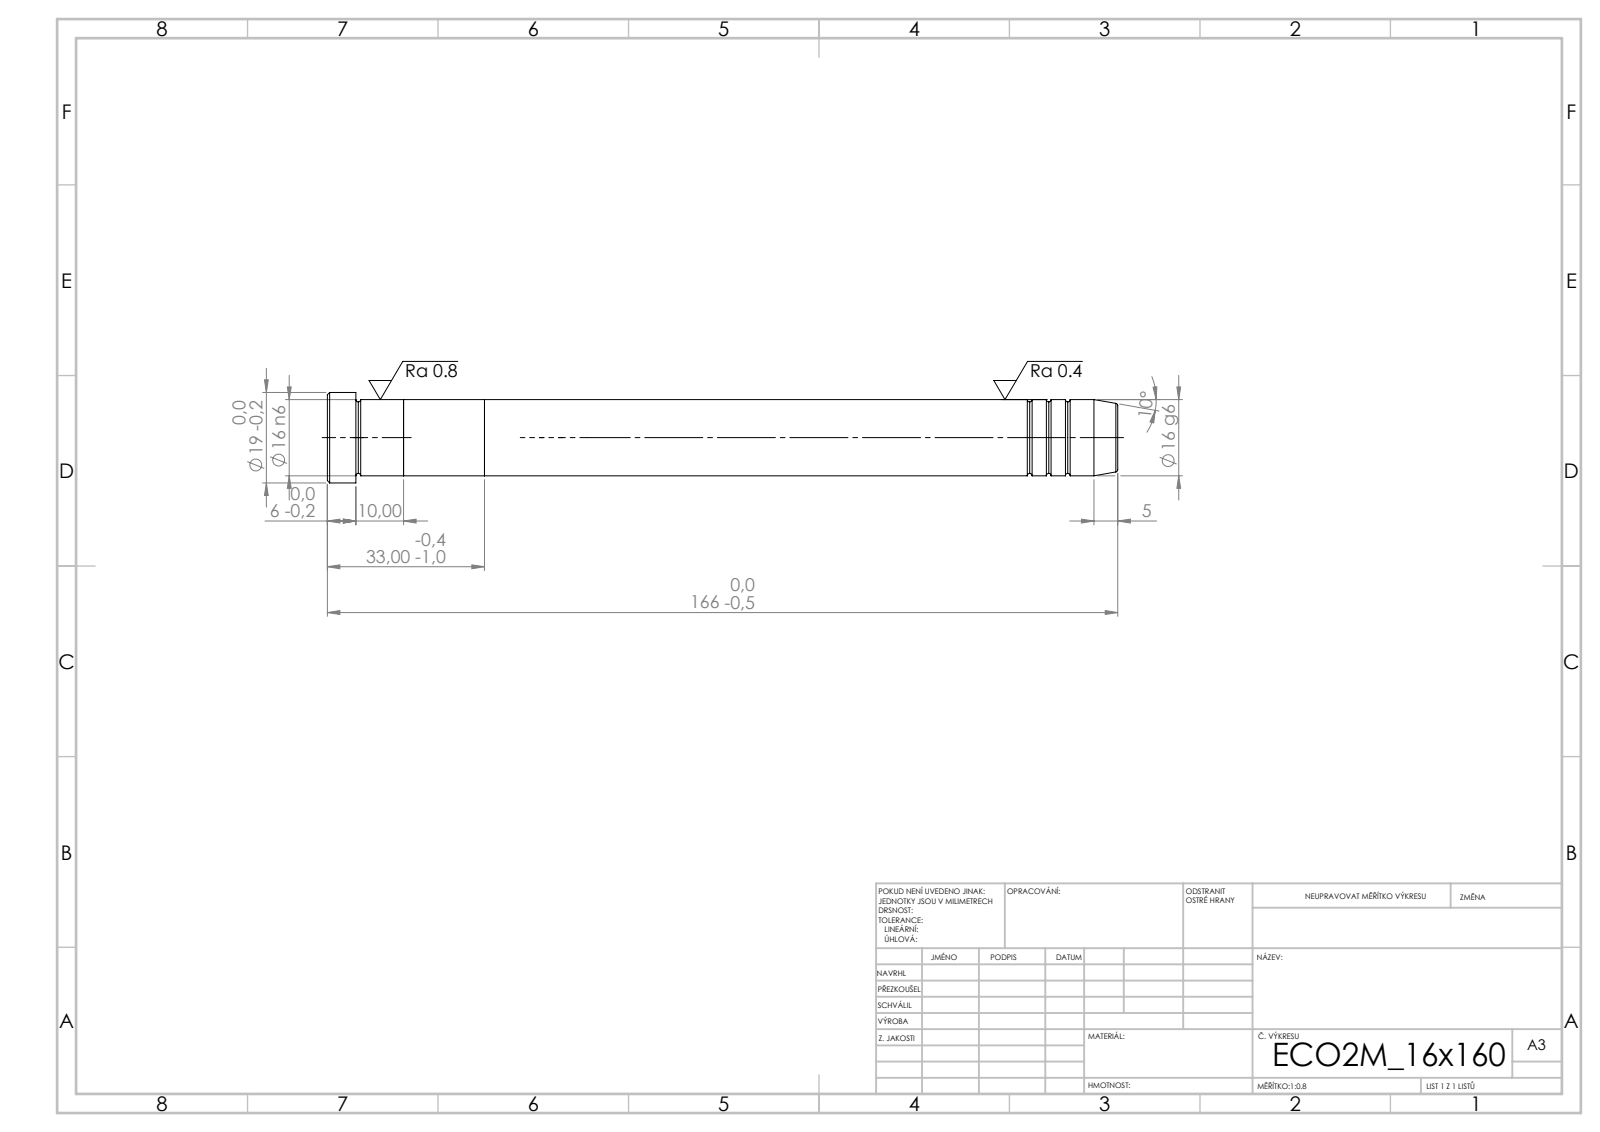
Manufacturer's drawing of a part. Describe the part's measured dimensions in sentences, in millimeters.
Its 3-D file was written by "SolidWorks 2019 (CONFIG_CONTROL_DESIGN)". It is 3 solids with 43 faces: 7 planar, 14 cylindrical and 22 other. Overall it measures 166 by 19 by 19 millimeters. Its volume is 33 679 cubic millimeters and its surface area 9 798 square millimeters. Round bosses or shafts: 1 of diameter 19, 1 of diameter 16. The main face-to-face distances are 17, 33, 16, 133, 150, 166, 160, 27, 10, 6.
